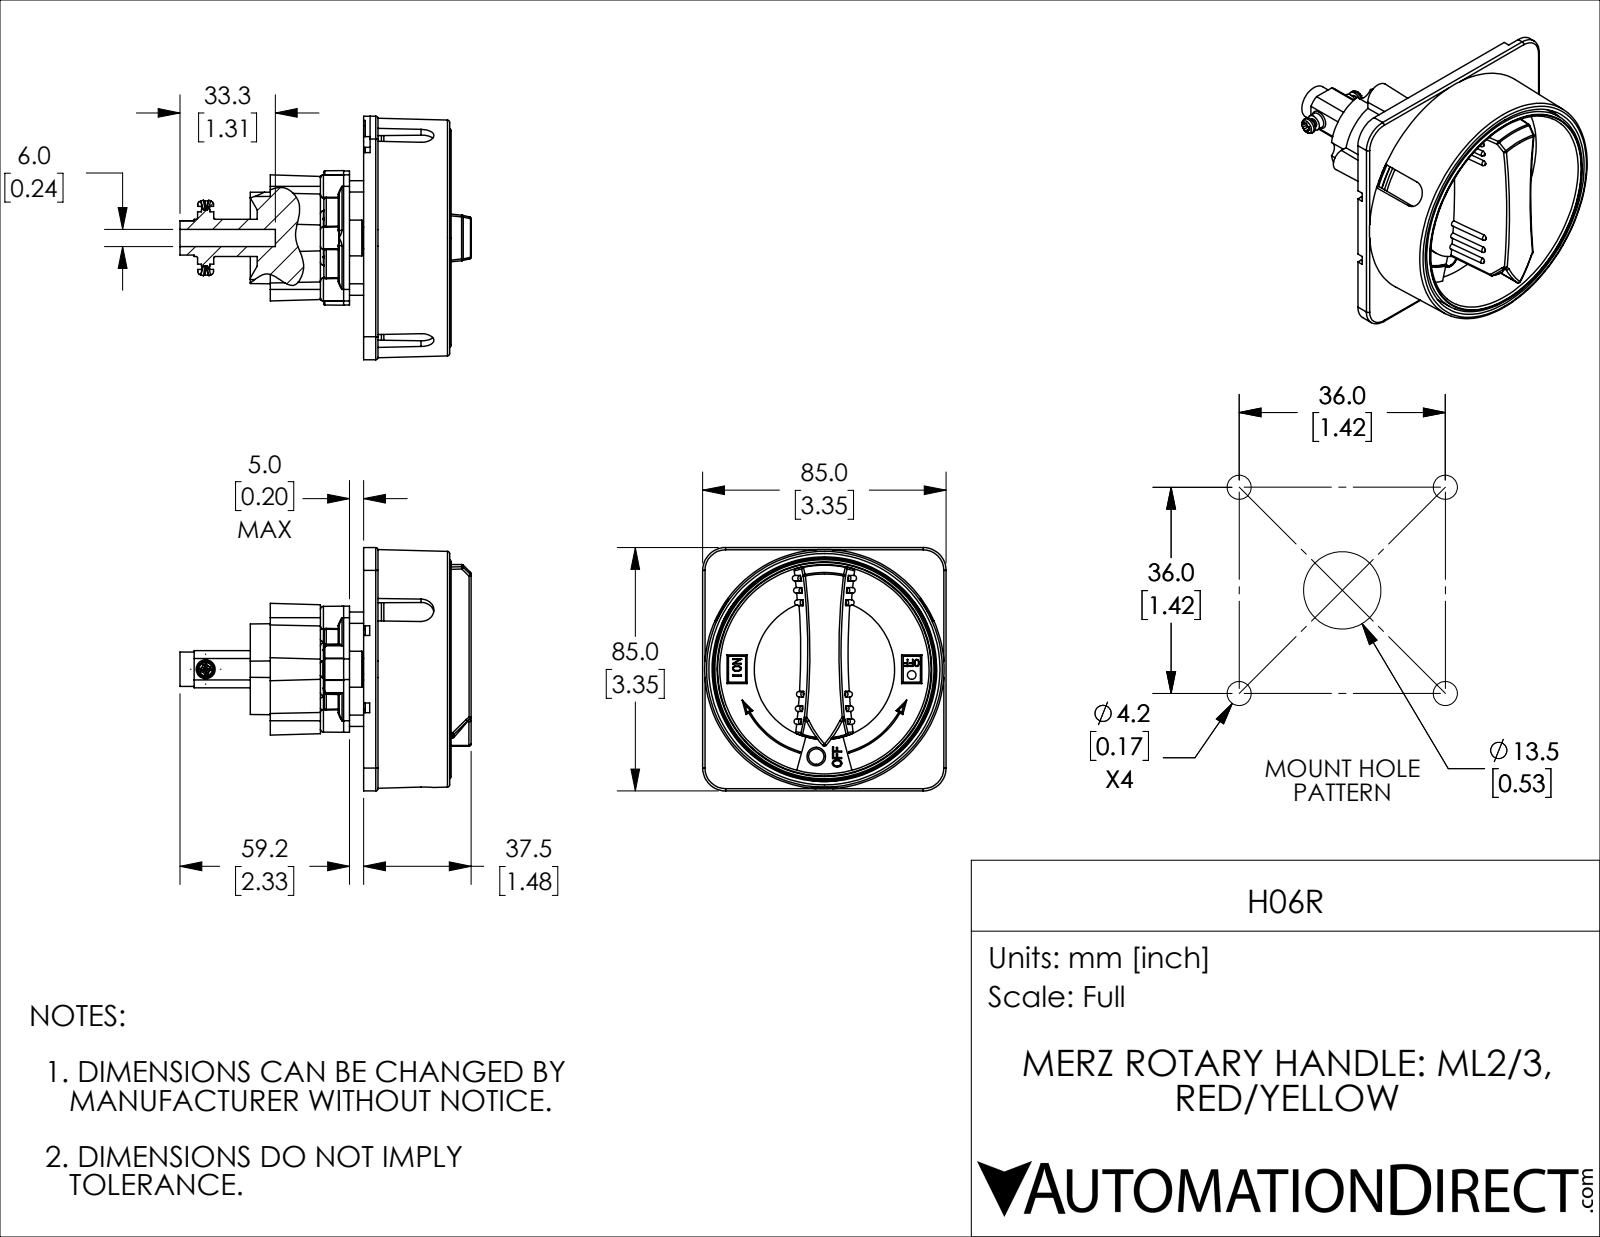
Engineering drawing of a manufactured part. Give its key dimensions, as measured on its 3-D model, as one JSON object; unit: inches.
{"part_name": "H06R", "step_written_by": "SolidWorks 2019 (AUTOMOTIVE_DESIGN)", "units": "inches", "bodies": {"solids": 1, "faces": 1642, "planar": 546, "cylindrical": 311, "other": 785}, "overall_size": [4.004, 3.346, 3.346], "volume_in3": 6.817, "surface_area_in2": 113.2, "round_holes": [[0.256, 1], [0.807, 1], [1.772, 1], [2.878, 1]], "round_bosses_or_shafts": [[0.197, 6], [0.157, 4], [0.118, 2], [3.051, 1], [3.012, 1], [1.929, 1], [1.882, 1], [1.024, 1]], "partial_cylinders_radius": [[0.012, 44], [0.031, 24], [0.01, 14], [0.157, 6], [0.055, 5], [0.315, 5], [0.008, 4], [0.039, 4]], "face_to_face_distances": [0.138, 0.079, 0.217, 0.059, 0.106, 0.031, 0.256, 0.177, 0.354, 0.335], "hole_center_spacings": [1.206]}
